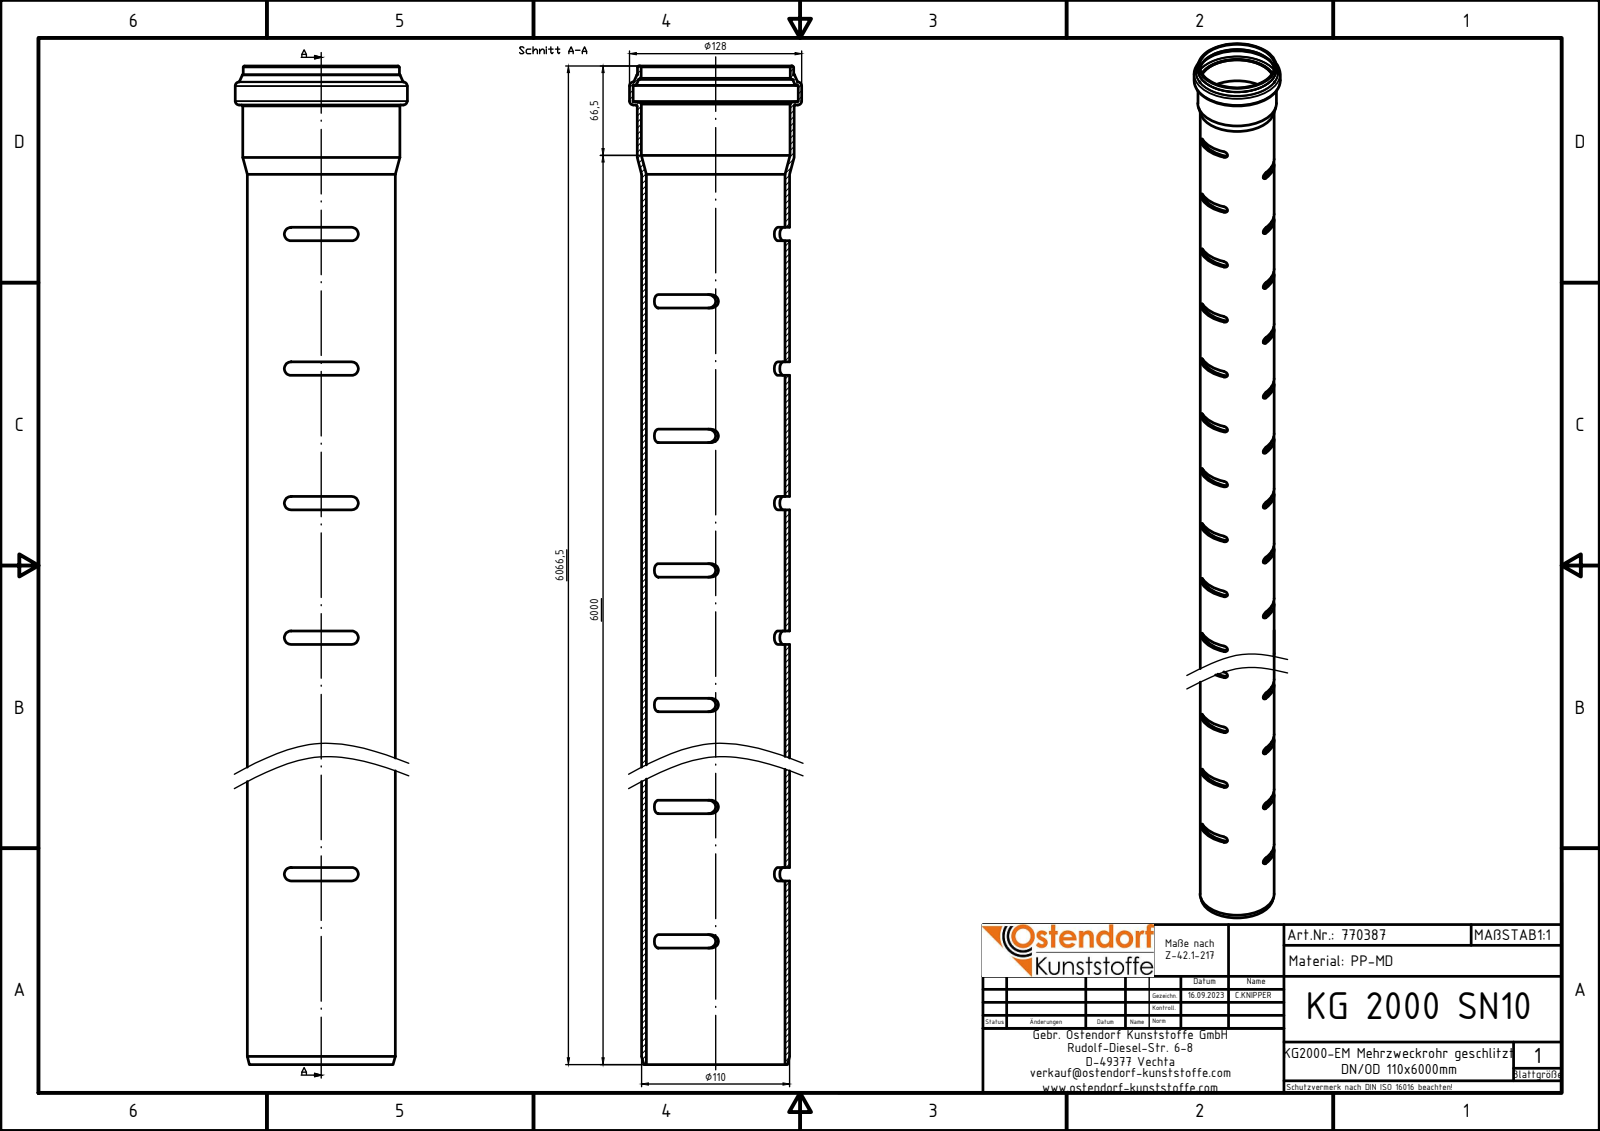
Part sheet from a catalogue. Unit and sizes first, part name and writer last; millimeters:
Units: millimetres
Overall size (bounding box): 6066.5 × 128 × 128
Round holes (diameter × count): ⌀102.96 ×1, ⌀110.5 ×1, ⌀110.9 ×1, ⌀122.8 ×1
Round bosses / shafts (diameter × count): ⌀128 ×1, ⌀116.7 ×1, ⌀116.1 ×1, ⌀110 ×1
Partial cylindrical surfaces — rounded edges, fillets, slot ends (radius × count): R5 ×236
Main face-to-face distances: 100, 200, 300, 400, 500, 600, 700, 800, 900, 1000
Volume: 6 912 000 mm³ · Surface area: 3 993 000 mm²
Bodies: 1 solid, 508 faces (241 planar, 245 cylindrical, 22 other)
Part name (STEP PRODUCT): 770387z
STEP written by: Autodesk Inventor 2024 (AUTOMOTIVE_DESIGN)
